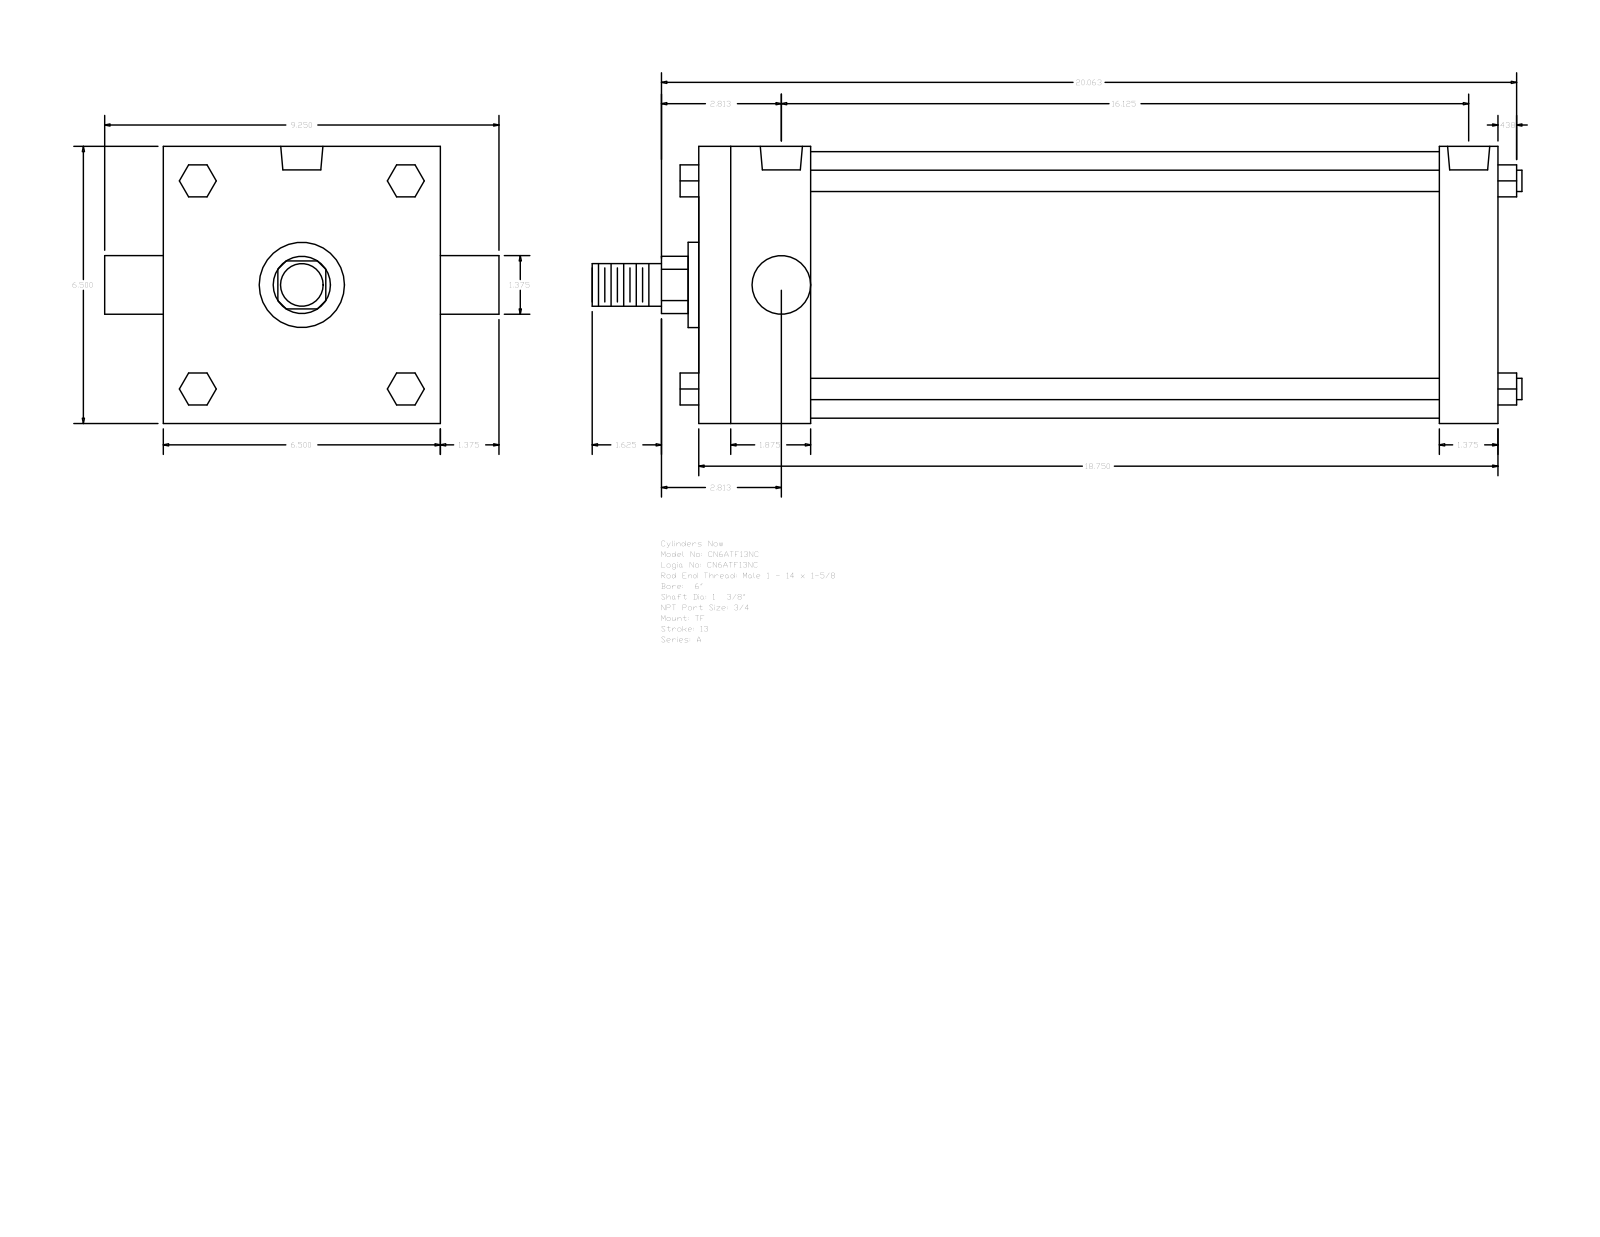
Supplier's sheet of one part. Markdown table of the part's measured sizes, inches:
| quantity | value |
| --- | --- |
| part name | A_TF__0600_1.375 |
| STEP written by | GSSL Pune (CONFIG_CONTROL_DESIGN) |
| units | inches |
| bodies | 0 solids, 120 faces (92 planar, 28 cylindrical, 0 other) |
| overall size | 21.813 × 9.25 × 6.5 |
| round holes (diameter × count) | 0.594 × 3, 0.989 × 2 |
| round bosses / shafts (diameter × count) | 0.5 × 4, 1.375 × 2, 6.25 × 1, 2 × 1, 1 × 1 |
| partial cylindrical surfaces (radius × count) | 0.672 × 1 |
| main face-to-face distances | 6.5, 18.75, 2.625, 16.125, 17.375, 14.75, 1.375, 0.75, 2.44, 4.226 |
| hole center spacings | 0.219, 15.906, 15.687, 16.125 |
